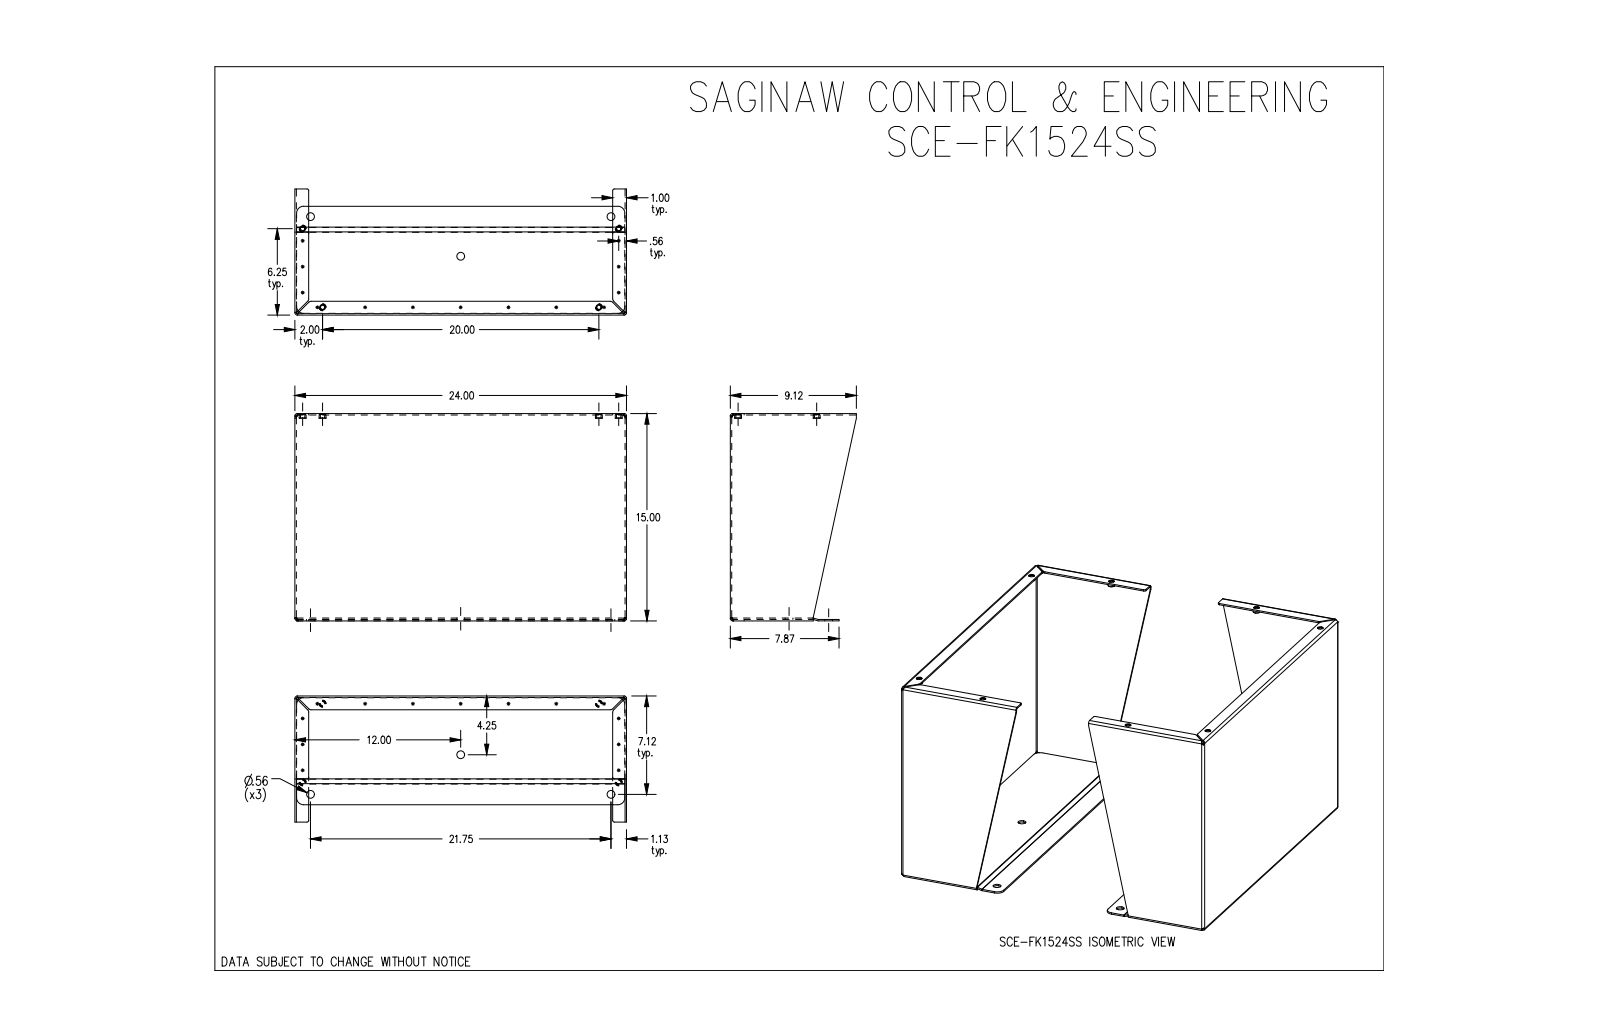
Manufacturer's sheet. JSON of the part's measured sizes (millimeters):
{"part_name": "SCE-FK1524SS", "step_written_by": "SolidWorks 2019 (CONFIG_CONTROL_DESIGN)", "units": "millimeters", "bodies": {"solids": 12, "faces": 286, "planar": 120, "cylindrical": 110, "other": 56}, "overall_size": [609.6, 609.6, 381], "volume_mm3": 2822000, "surface_area_mm2": 2164000, "round_holes": [[7.9, 8], [10.5, 8], [14.3, 6]], "round_bosses_or_shafts": [[12.7, 8], [10.5, 8]], "partial_cylinders_radius": [[4.2, 16], [1.6, 12], [3.2, 8], [5.6, 8], [12.7, 8], [1.6, 6]], "face_to_face_distances": [2.6, 607, 604.3, 609.6, 2.6, 378.3, 375.7, 378.4, 5.2, 375.6], "hole_center_spacings": [26.3, 149, 168, 270.4, 270.7, 294.9, 415.1, 438.1]}
